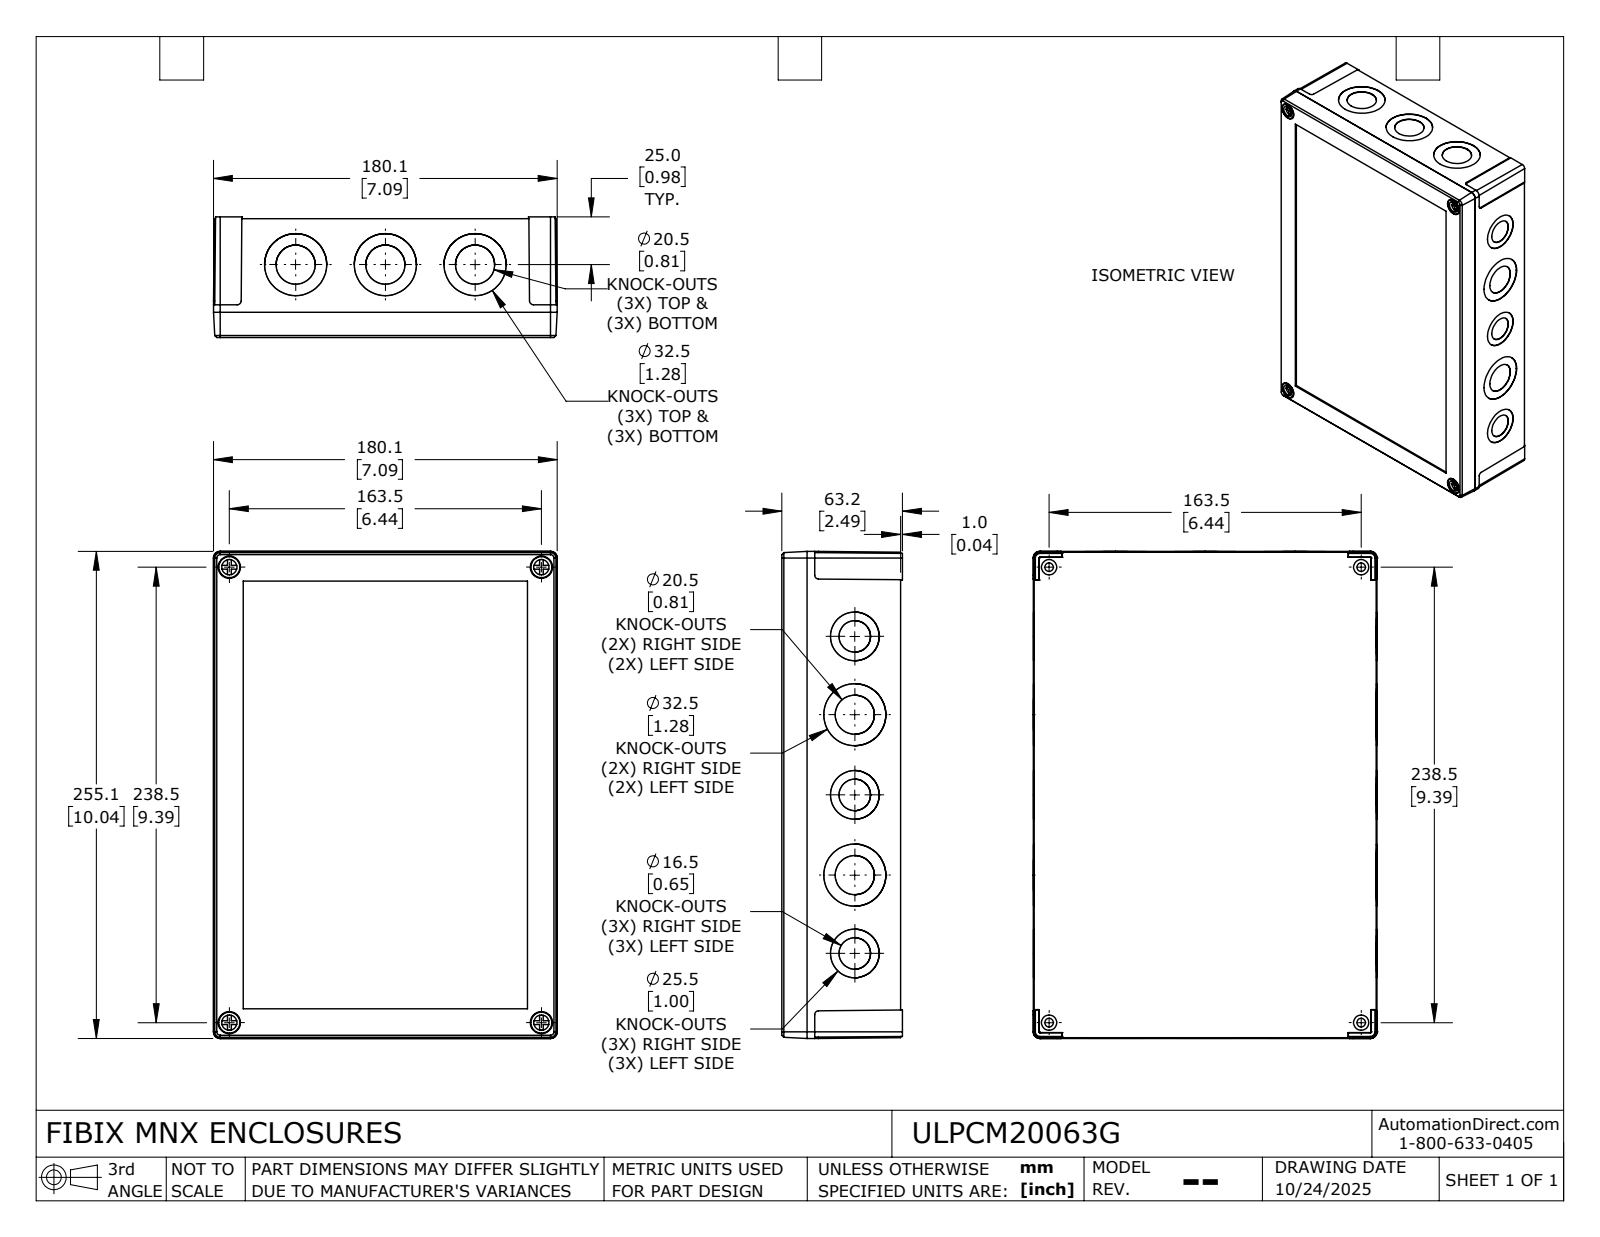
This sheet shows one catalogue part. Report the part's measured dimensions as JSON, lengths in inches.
{"part_name": "ULPCM20063G_Default", "step_written_by": "SolidWorks 2024 (CONFIG_CONTROL_DESIGN)", "units": "inches", "bodies": {"solids": 6, "faces": 795, "planar": 397, "cylindrical": 350, "other": 48}, "overall_size": [10.043, 7.091, 2.488], "volume_in3": 36.25, "surface_area_in2": 476.9, "round_holes": [[0.126, 40], [0.094, 20], [0.157, 20], [0.807, 10], [1.28, 10], [0.65, 6], [1.004, 6], [0.177, 4], [0.315, 4], [0.457, 4]], "round_bosses_or_shafts": [[0.315, 16], [0.433, 4], [0.283, 4], [0.276, 4]], "partial_cylinders_radius": [[0.112, 6], [0.042, 4], [0.079, 4], [0.197, 4], [0.046, 2], [48.383, 1]], "face_to_face_distances": [0.118, 2.409, 2.291, 0.138, 2.272, 2.154, 0.165, 0.039, 0.177, 2.449], "hole_center_spacings": [4.921, 1.939, 1.969, 5.046, 3.937, 0.812, 0.872, 1.046]}
